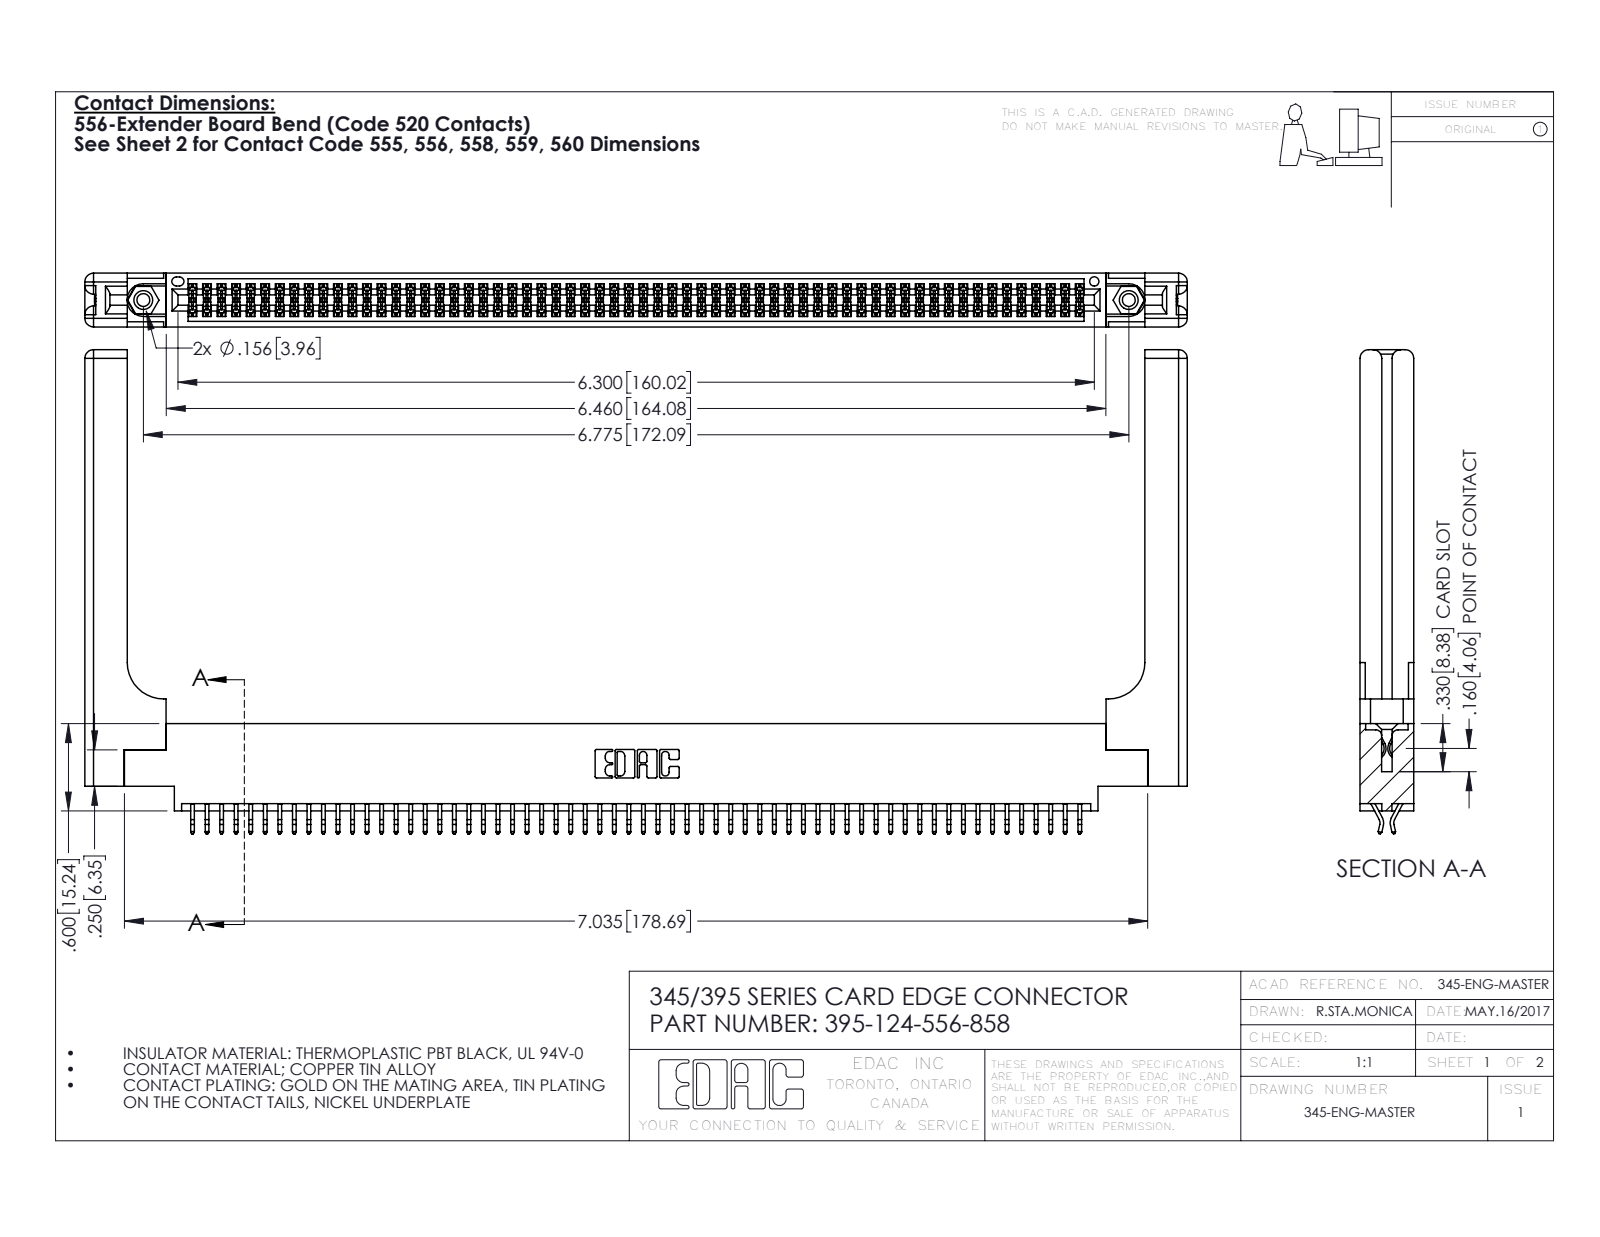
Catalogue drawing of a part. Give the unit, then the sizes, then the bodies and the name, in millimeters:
Units: millimetres
Overall size (bounding box): 192.5 × 84.5 × 9.4
Round holes (diameter × count): ⌀2.3 ×2, ⌀3.2 ×2, ⌀4 ×2, ⌀1.6 ×1
Round bosses / shafts (diameter × count): ⌀3.9 ×2
Partial cylindrical surfaces — rounded edges, fillets, slot ends (radius × count): R0.2 ×186, R0.3 ×22, R1.5 ×16, R0.2 ×6, R0.8 ×6, R0.7 ×3, R0.3 ×2, R0.4 ×2
Main face-to-face distances: 1.8, 7.6, 9.4, 0.6, 2.5, 6.9, 5.1, 5.7, 4.4, 3.8
Hole centre spacings: 6.9, 166.1, 172.1
Volume: 27 240 mm³ · Surface area: 33 230 mm²
Bodies: 129 solids, 7330 faces (4820 planar, 2450 cylindrical, 60 other)
Part name (STEP PRODUCT): 345-292-001_556 Tail; 395-124-556-858; 345-250-001_345-250-001-102; 345-220-058_345-220-058 (+1 more)
STEP written by: SolidWorks 2016 (CONFIG_CONTROL_DESIGN)
